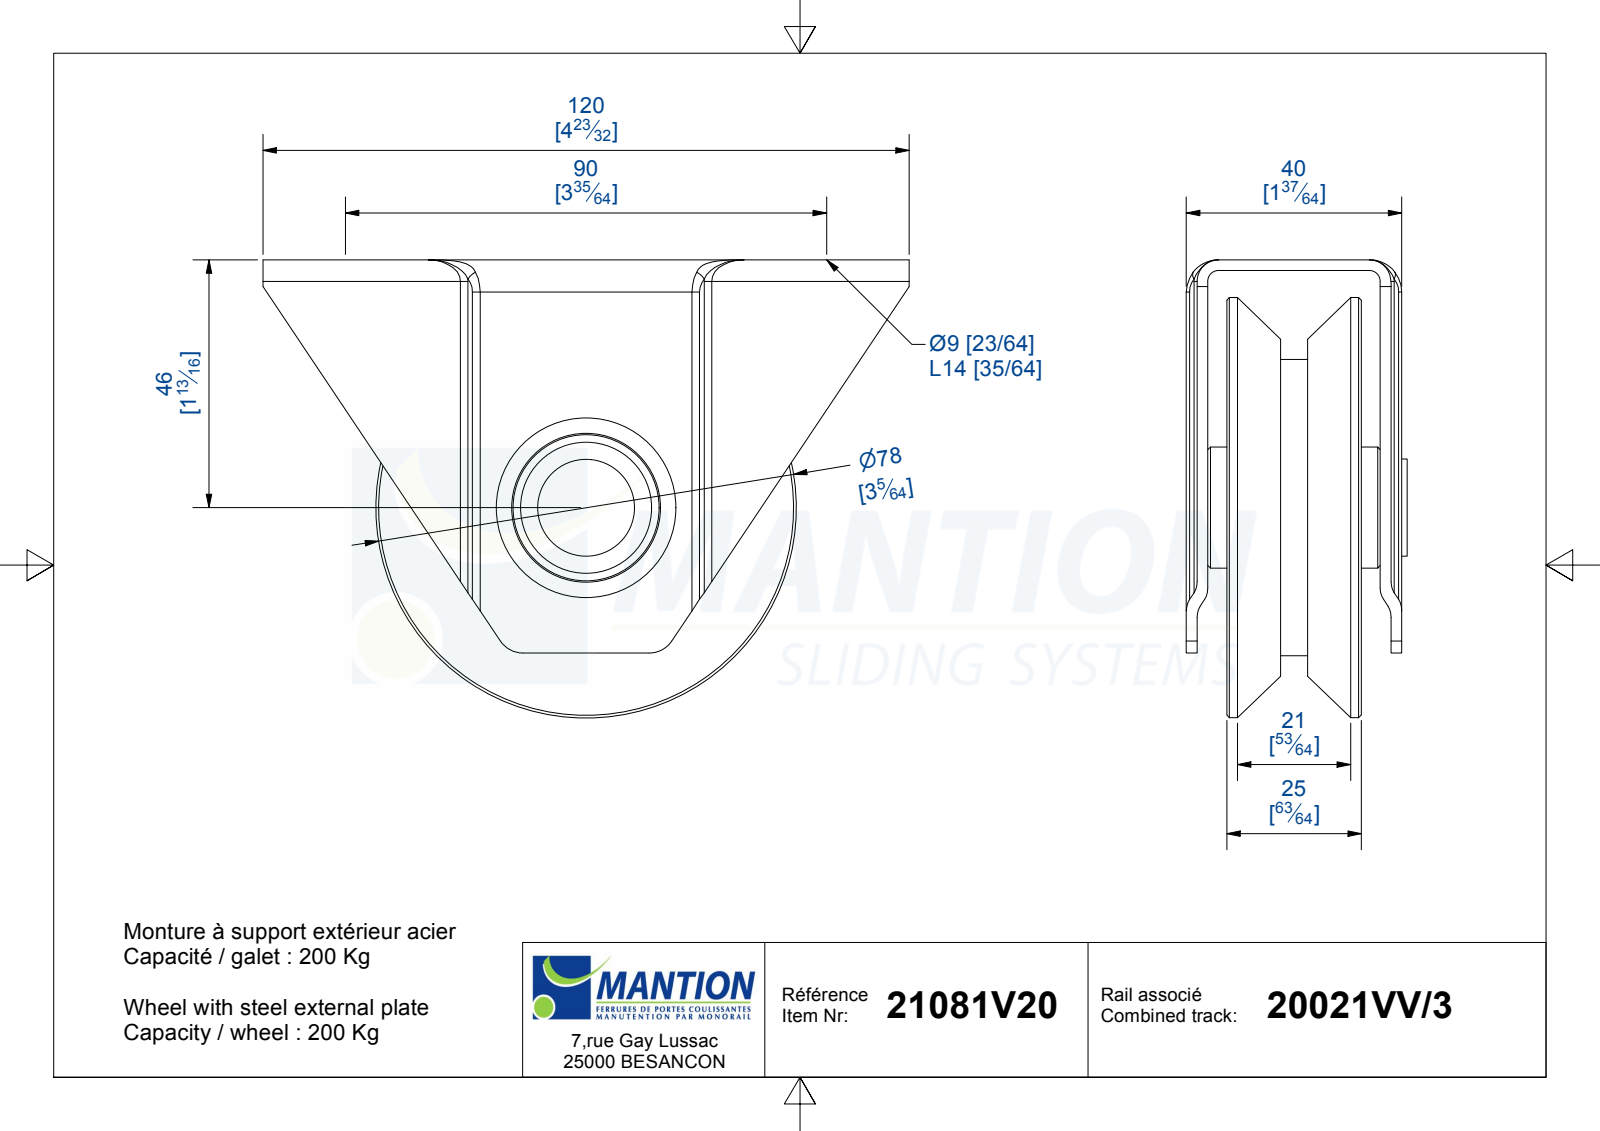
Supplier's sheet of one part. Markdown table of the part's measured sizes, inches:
| quantity | value |
| --- | --- |
| part name | 21081V20; 19758; 19744; local.DIN.249.610.5 (+2 more) |
| STEP written by | Autodesk Inventor 2019 (AUTOMOTIVE_DESIGN) |
| units | inches |
| bodies | 13 solids, 280 faces (95 planar, 60 cylindrical, 125 other) |
| overall size | 4.724 × 3.346 × 1.614 |
| volume | 6.665 in³ |
| surface area | 96.6 in² |
| round holes (diameter × count) | 0.413 × 1, 0.559 × 1, 0.571 × 1, 1.28 × 1, 1.437 × 1, 1.575 × 1, 1.591 × 1, 1.772 × 1 |
| round bosses / shafts (diameter × count) | 3.071 × 1, 2.165 × 1, 0.965 × 1, 0.886 × 1, 0.709 × 1, 0.669 × 1, 0.547 × 1 |
| partial cylindrical surfaces (radius × count) | 0.079 × 18, 0.157 × 4, 0.177 × 4, 0.197 × 2, 0.236 × 2 |
| main face-to-face distances | 0.079, 1.417, 0.138, 0.217, 1.201, 1.339, 1.122, 0.157, 0.295, 1.28 |
